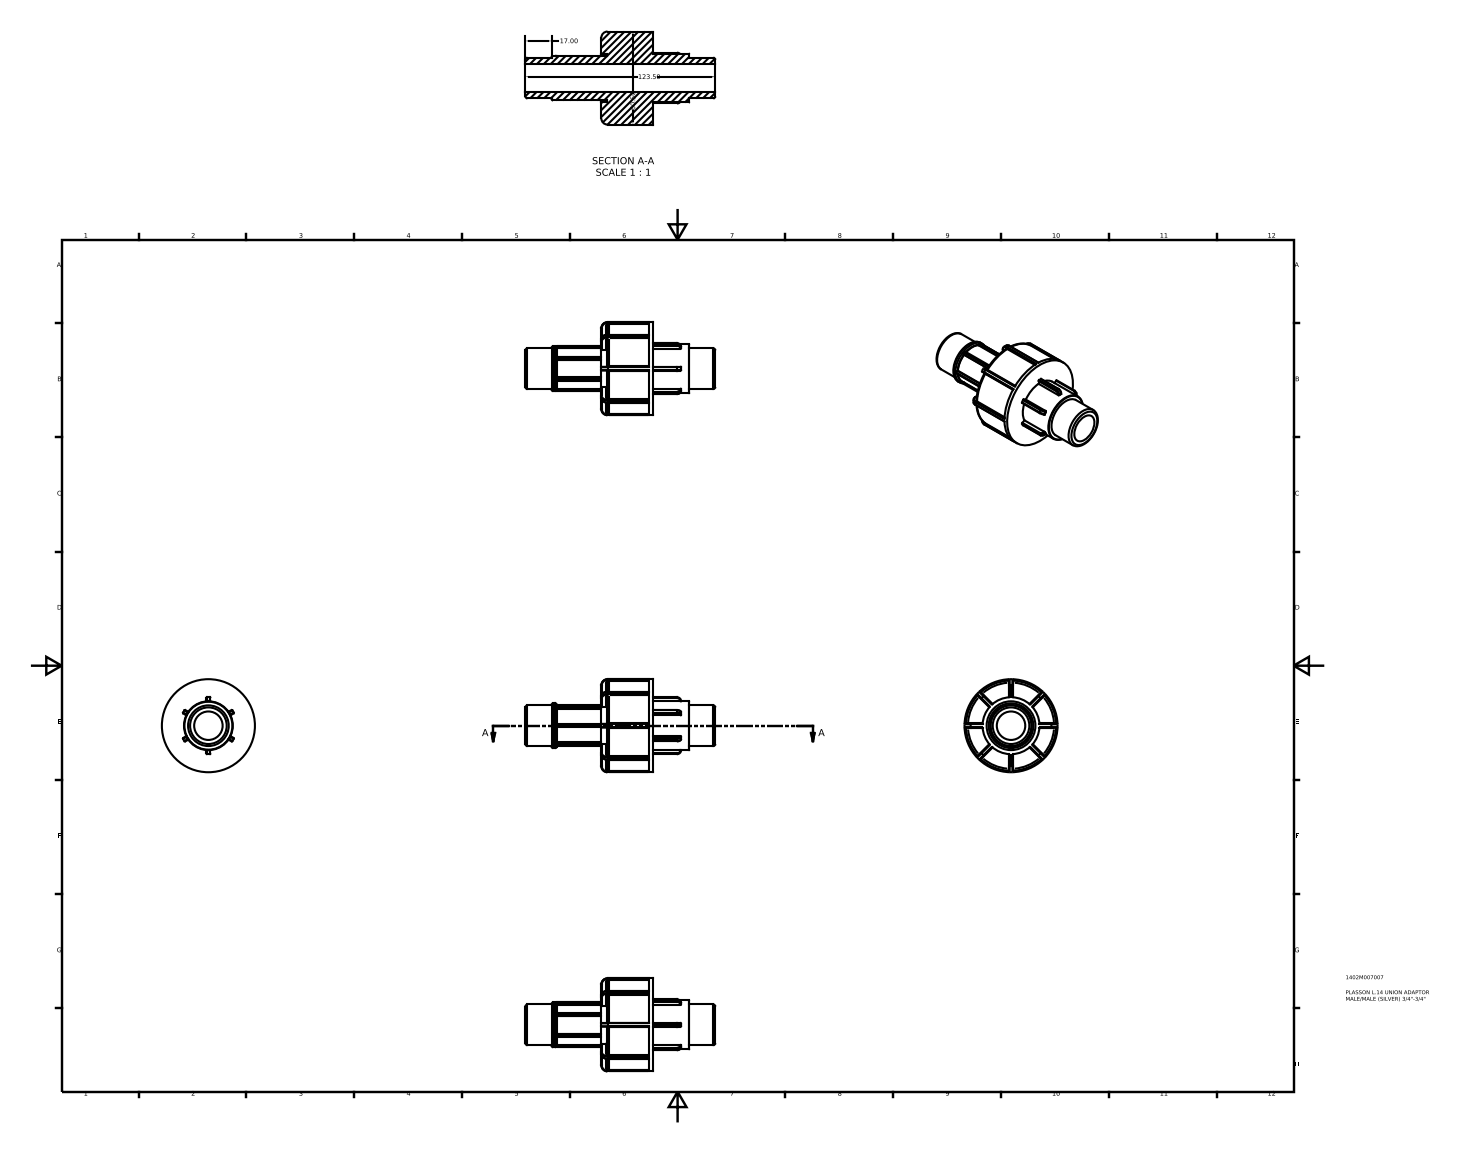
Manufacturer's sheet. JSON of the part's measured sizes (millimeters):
{"part_name": "1402M007007", "step_written_by": "Autodesk Inventor 2015 (AUTOMOTIVE_DESIGN)", "units": "millimeters", "bodies": {"solids": 1, "faces": 297, "planar": 92, "cylindrical": 140, "other": 65}, "overall_size": [123.5, 60.5, 60.5], "volume_mm3": 108897, "surface_area_mm2": 28472, "round_holes": [[18.51, 1], [31.73, 1]], "round_bosses_or_shafts": [[60.5, 1], [58.69, 1], [37.02, 1], [29.09, 1], [26.44, 1]], "partial_cylinders_radius": [[0.3, 52], [0.53, 18], [1, 12], [2.64, 6]], "face_to_face_distances": [29.94, 3.4, 33.34, 2.42, 2.64, 57.1, 53.7, 23.76, 106.5, 17]}
